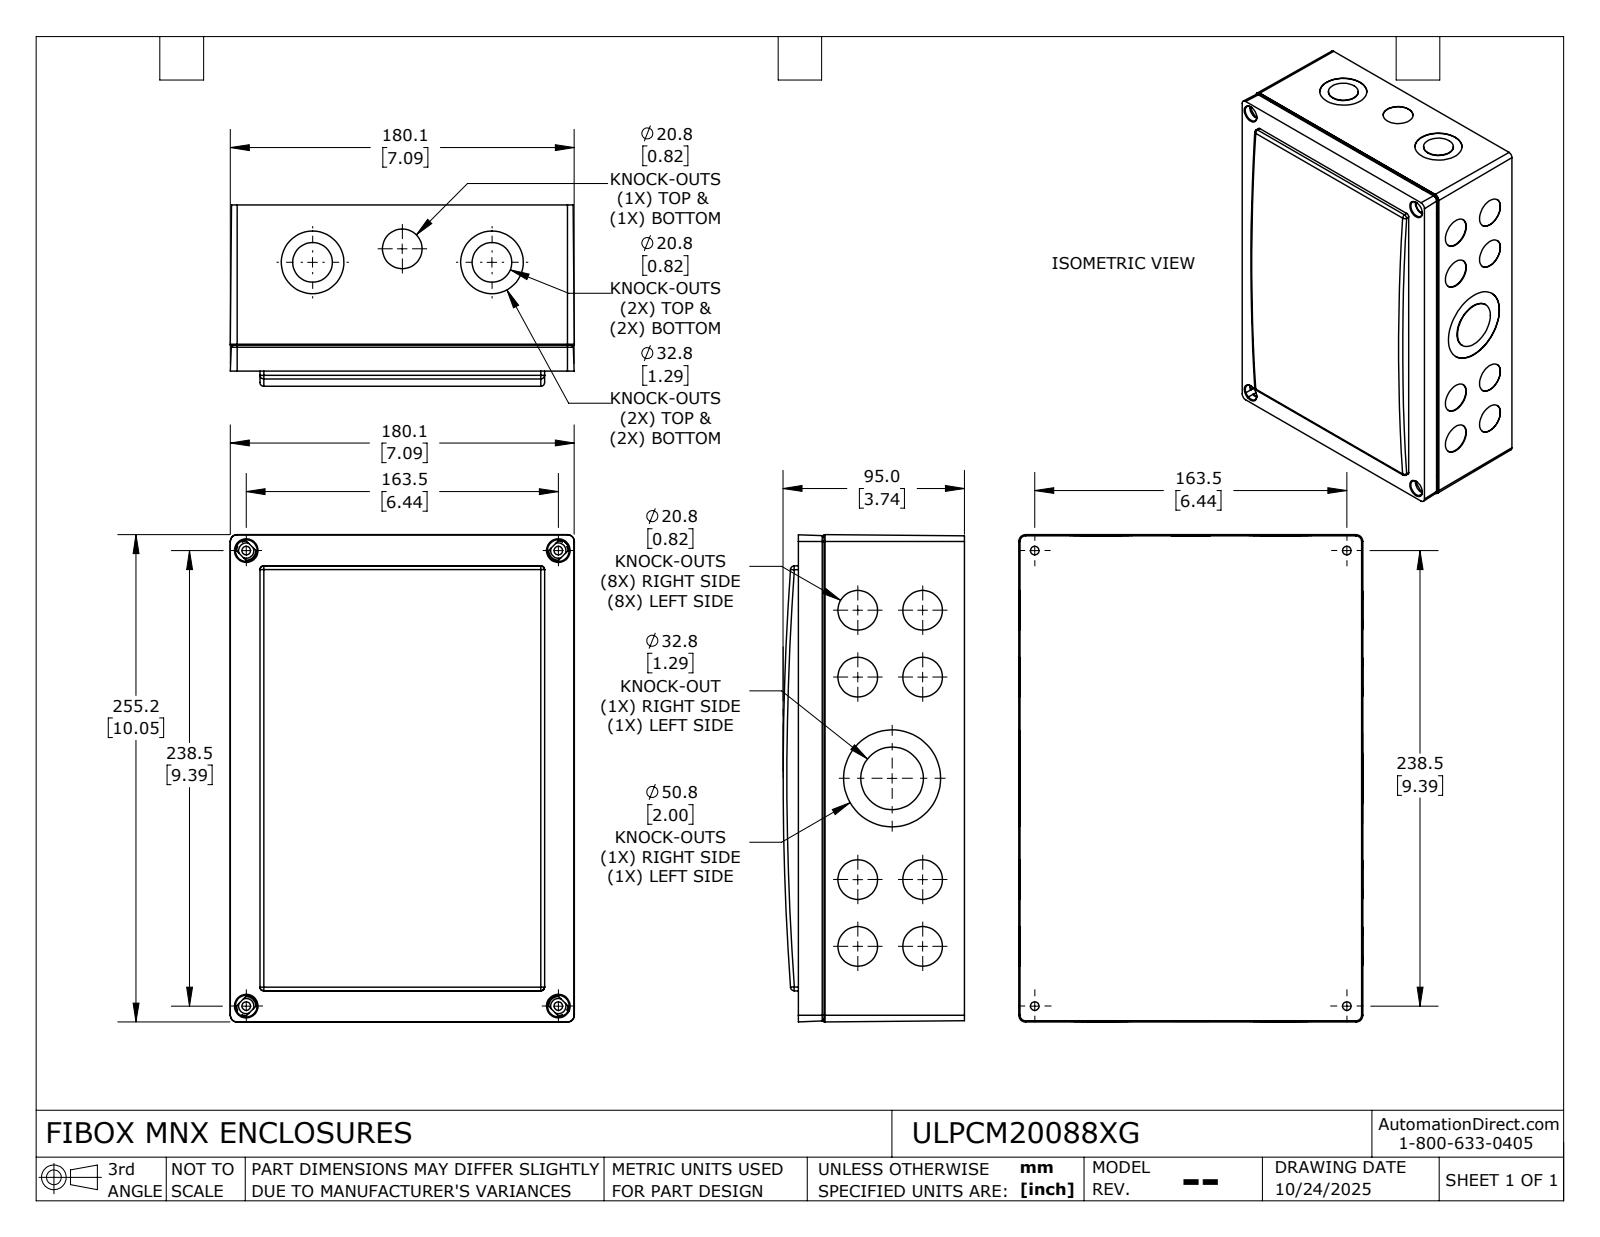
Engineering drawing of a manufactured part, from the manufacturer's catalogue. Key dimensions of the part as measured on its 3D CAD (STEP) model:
Part name (STEP PRODUCT): ULPCM20088XG
STEP written by: SolidWorks 2024 (AUTOMOTIVE_DESIGN)
Units: millimetres
Bodies: 2 solids, 339 faces (177 planar, 122 cylindrical, 40 other)
Overall size (bounding box): 255.17 × 180.17 × 95
Volume: 709 907 mm³ · Surface area: 340 472 mm²
Round holes (diameter × count): ⌀3.2 ×20, ⌀4.5 ×4, ⌀8 ×4, ⌀11.34 ×2, ⌀11.38 ×1, ⌀11.39 ×1
Round bosses / shafts (diameter × count): ⌀7.19 ×12, ⌀9.18 ×8, ⌀2.52 ×8
Partial cylindrical surfaces — rounded edges, fillets, slot ends (radius × count): R2 ×12, R1.38 ×8, R4.02 ×8, R2.9 ×4, R3.5 ×4, R5 ×4, R5.58 ×4, R8.22 ×4
Main face-to-face distances: 3, 14, 70, 73, 87, 84, 147.91, 0.5, 73.5, 70.5
Hole centre spacings: 49.24, 128.16, 125, 20.62, 22.15, 26.58, 33.85, 38.3
